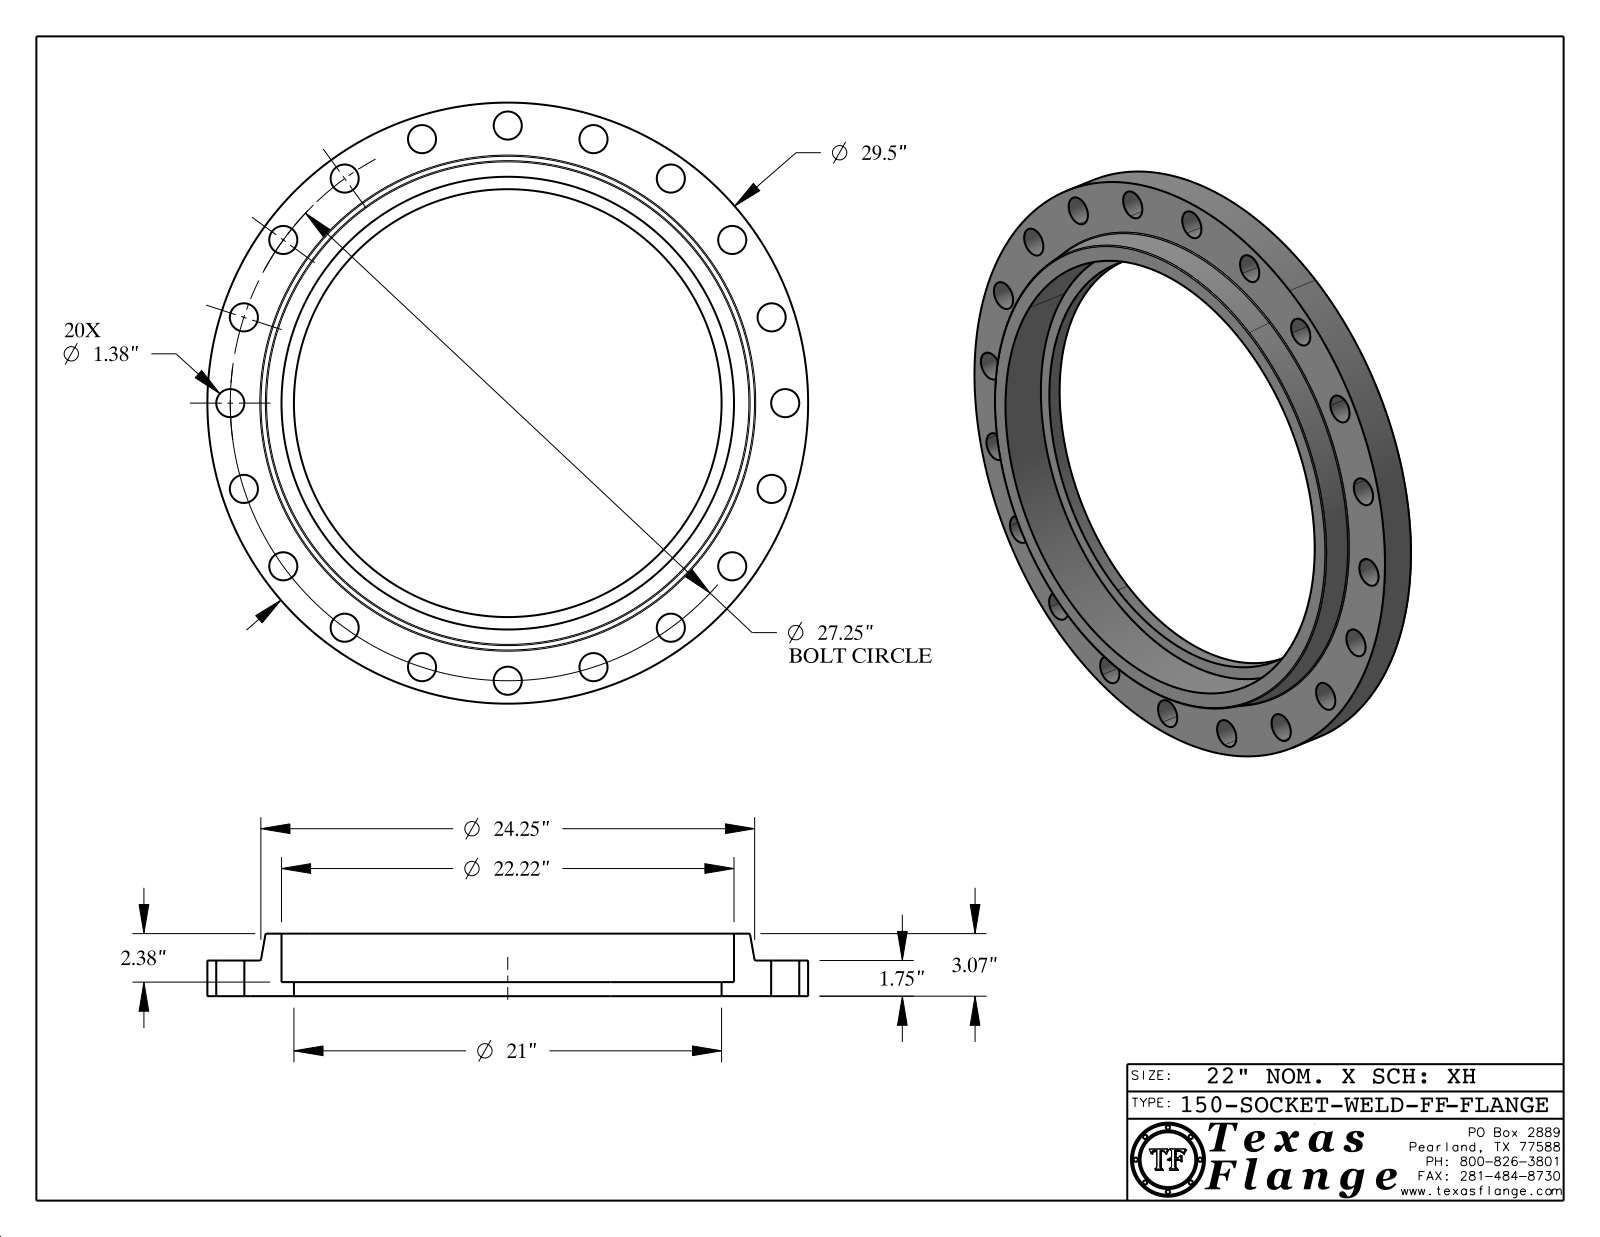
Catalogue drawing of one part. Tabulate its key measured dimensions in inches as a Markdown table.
| quantity | value |
| --- | --- |
| part name | 150-SOCKET-WELD-FF |
| STEP written by | CATIA V5 STEP AP214 (AUTOMOTIVE_DESIGN) |
| units | inches |
| bodies | 1 solid, 442 faces (370 planar, 66 cylindrical, 6 other) |
| overall size | 29.5 × 29.5 × 3.07 |
| volume | 579.9 in³ |
| surface area | 1 221 in² |
| round holes (diameter × count) | 1.38 × 20, 0.495 × 1, 21 × 1, 22.22 × 1 |
| round bosses / shafts (diameter × count) | 0.03 × 8, 29.5 × 1, 0.39 × 1 |
| main face-to-face distances | 1.75, 3.07, 1.32, 0.69, 1.06, 2.38, 1.735, 1.045, 0.015, 1.335 |
| hole center spacings | 13.625, 19.269, 25.917, 8.421, 12.371, 4.263, 16.017, 22.046 |
